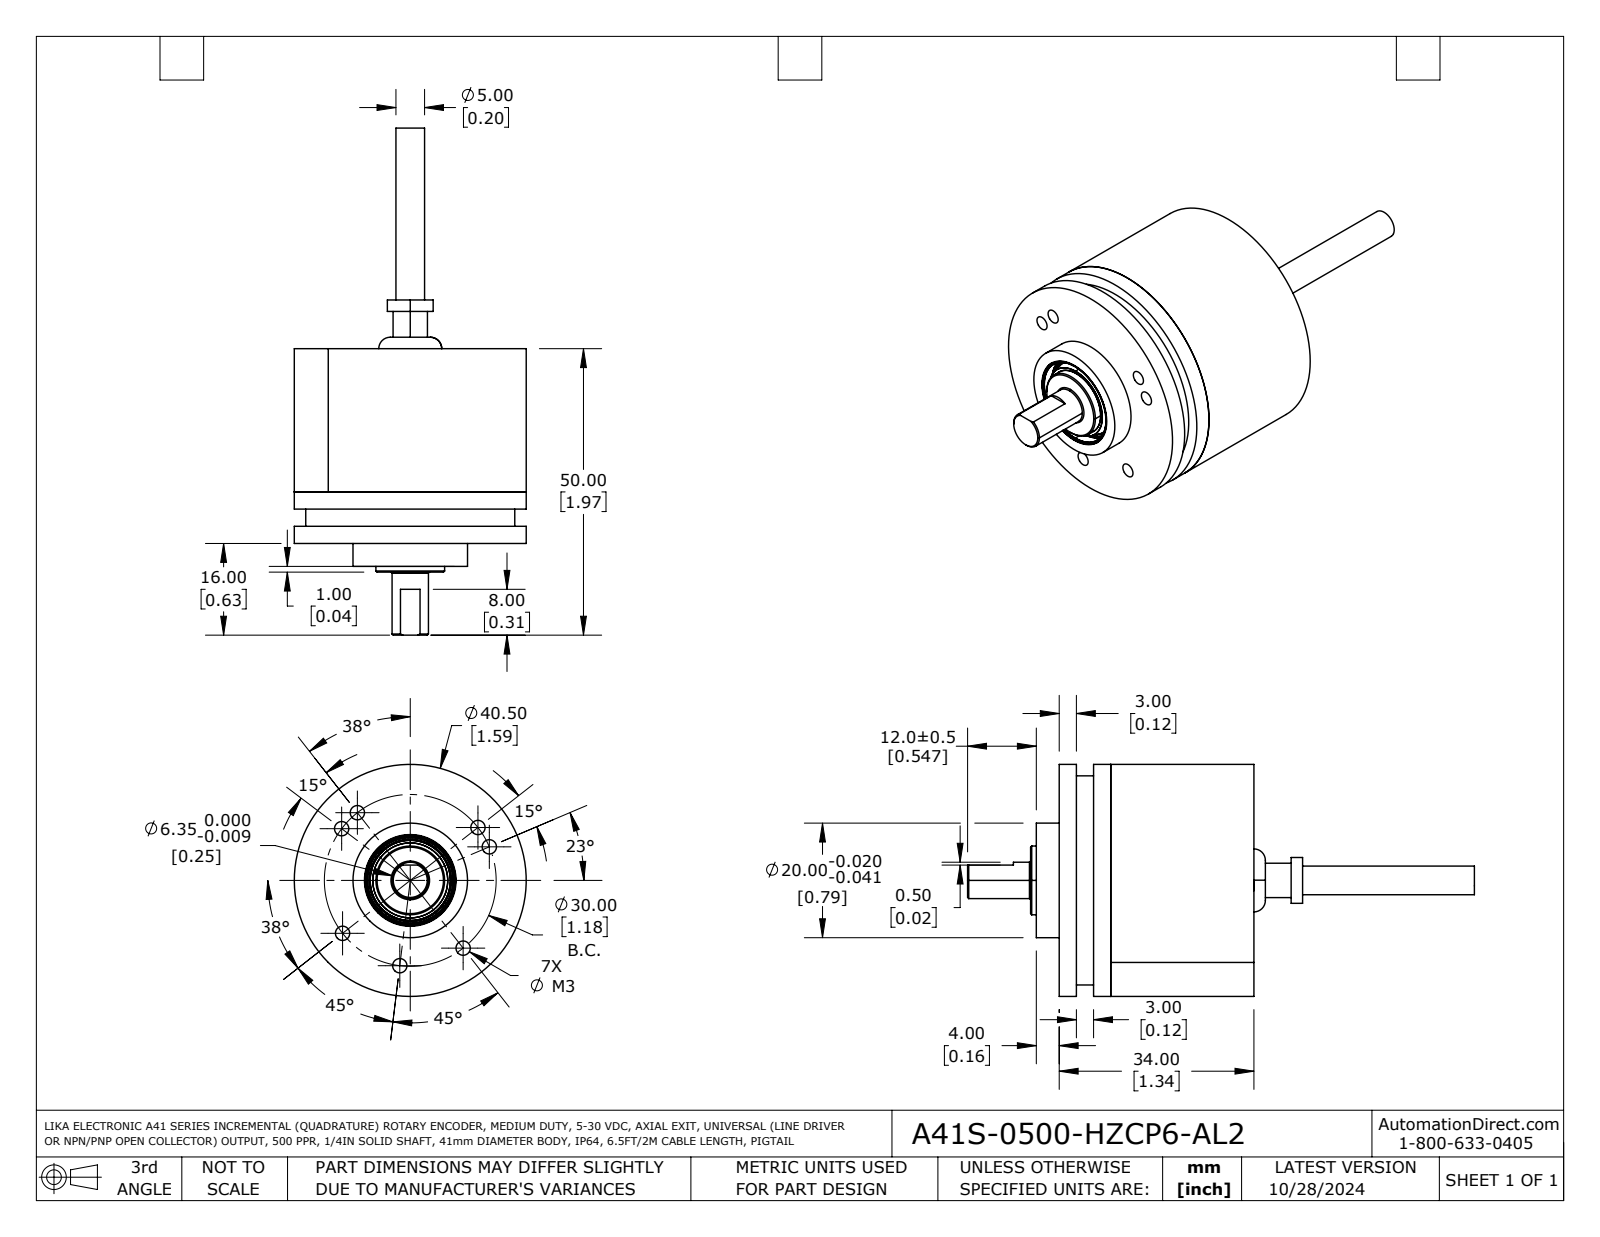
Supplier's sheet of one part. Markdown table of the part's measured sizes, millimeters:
| quantity | value |
| --- | --- |
| part name | A41S-0500-HZCP6-AL2 |
| STEP written by | SolidWorks 2021 (AUTOMOTIVE_DESIGN) |
| units | millimeters |
| bodies | 11 solids, 422 faces (76 planar, 145 cylindrical, 201 other) |
| overall size | 88.5 × 40.5 × 40.5 |
| volume | 19 250 mm³ |
| surface area | 18 250 mm² |
| round holes (diameter × count) | 1.6 × 7, 2.5 × 7, 4 × 3, 2.2 × 2, 4.3 × 1, 7.5 × 1, 13 × 1, 15.3 × 1, 15.5 × 1, 16 × 1, 38.5 × 1 |
| round bosses / shafts (diameter × count) | 2 × 2, 40.5 × 1, 38 × 1, 37 × 1, 36.5 × 1, 20 × 1, 12 × 1, 8 × 1 |
| partial cylindrical surfaces (radius × count) | 1 × 14, 0.2 × 6, 0.2 × 2 |
| main face-to-face distances | 3, 34, 11, 23, 31, 2, 22, 25, 20, 1 |
| hole center spacings | 15, 17, 21.2, 2.8, 3, 21.3, 24, 31.9 |
